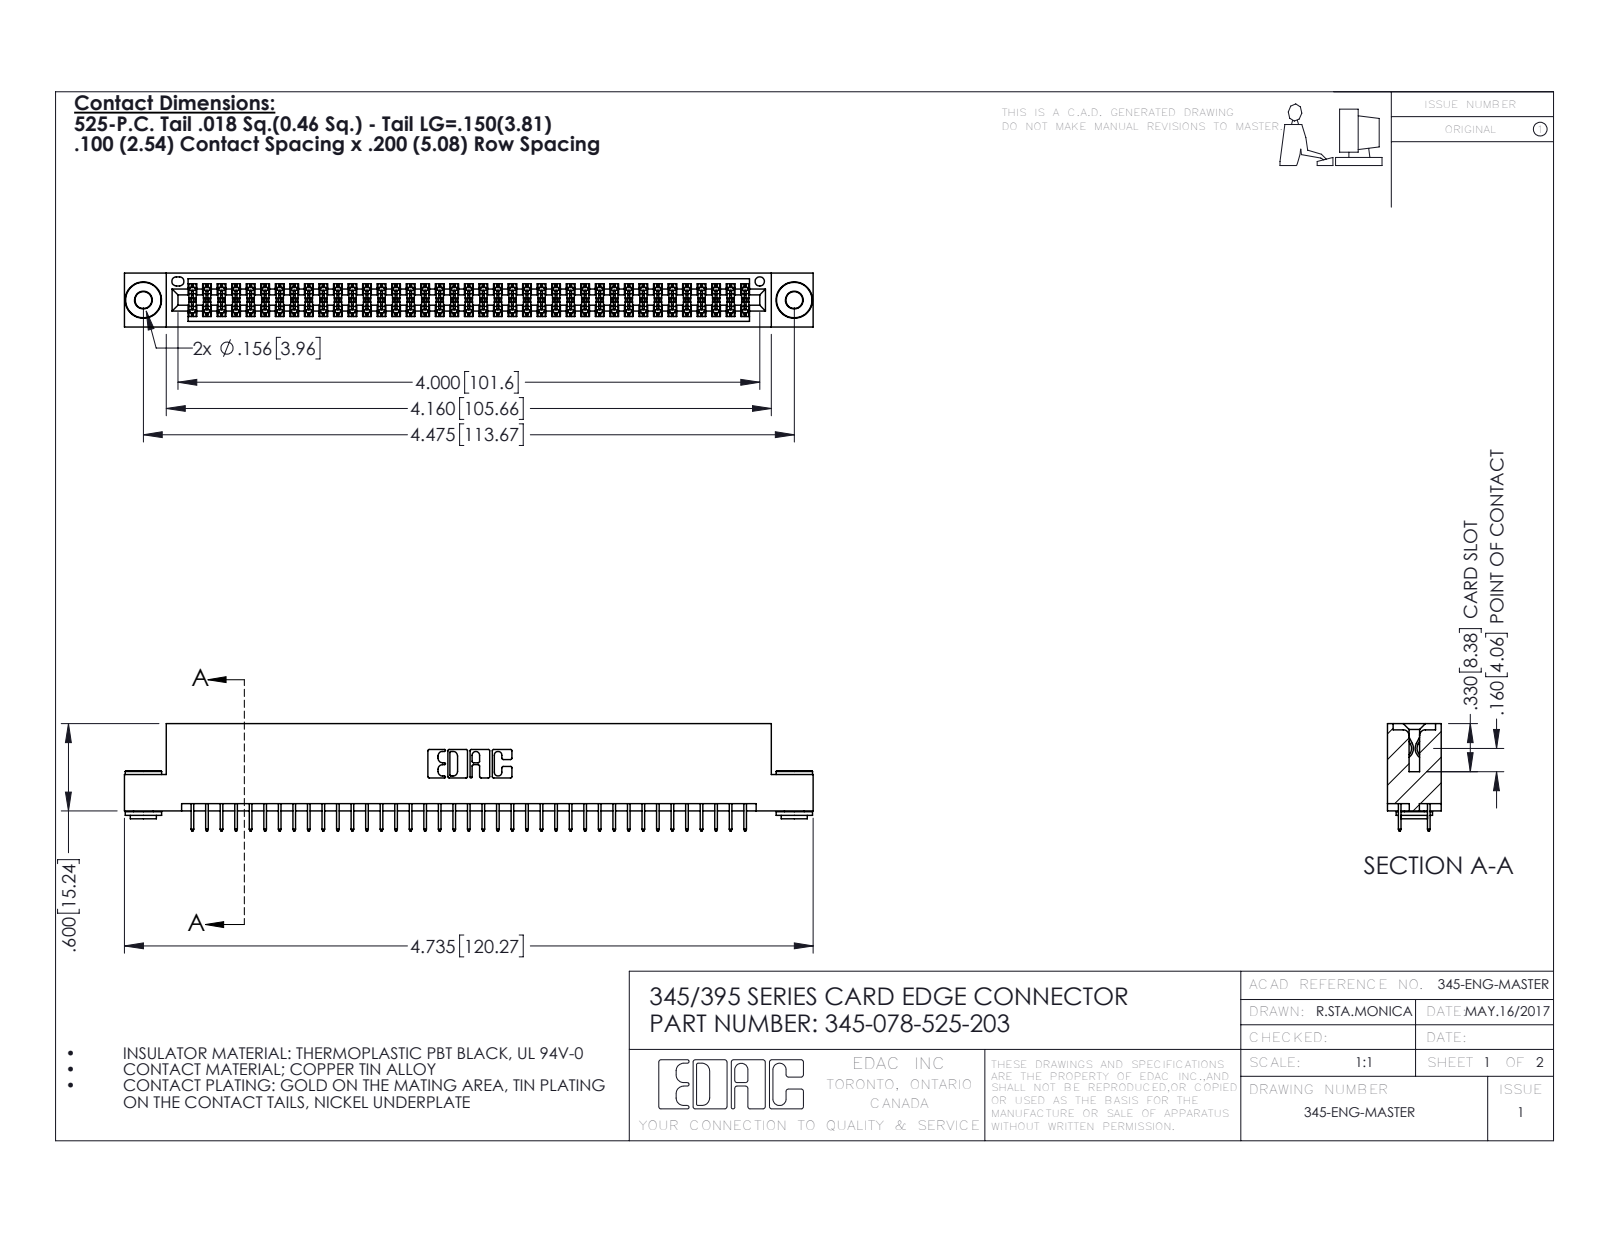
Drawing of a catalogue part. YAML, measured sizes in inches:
part_name: "345-250-002_345-250-002-102; 345-292-001_345-293-125; 345 Part_Flush Mounting Lugs - 0.156 Dia-TH; 345-078-525-203"
step_written_by: "SolidWorks 2020 (CONFIG_CONTROL_DESIGN)"
units: inches
bodies: {solids: 81, faces: 4376, planar: 3132, cylindrical: 1236, other: 8}
overall_size: [4.735, 0.737, 0.37]
volume: 0.705
surface_area: 26.08
round_holes:
  - {diameter: 0.116, count: 2}
  - {diameter: 0.156, count: 2}
  - {diameter: 0.064, count: 1}
round_bosses_or_shafts:
  - {diameter: 0.25, count: 2}
  - {diameter: 0.18, count: 2}
  - {diameter: 0.136, count: 2}
partial_cylinders:
  - {radius: 0.006, count: 117}
  - {radius: 0.01, count: 22}
  - {radius: 0.007, count: 6}
  - {radius: 0.031, count: 6}
  - {radius: 0.026, count: 3}
  - {radius: 0.014, count: 2}
  - {radius: 0.019, count: 2}
  - {radius: 0.022, count: 2}
face_to_face_distances: [0.072, 0.298, 0.2, 0.37, 0.025, 0.098, 0.272, 0.225, 0.072, 0.175]
hole_center_spacings: [0.27, 4.239, 4.475]
